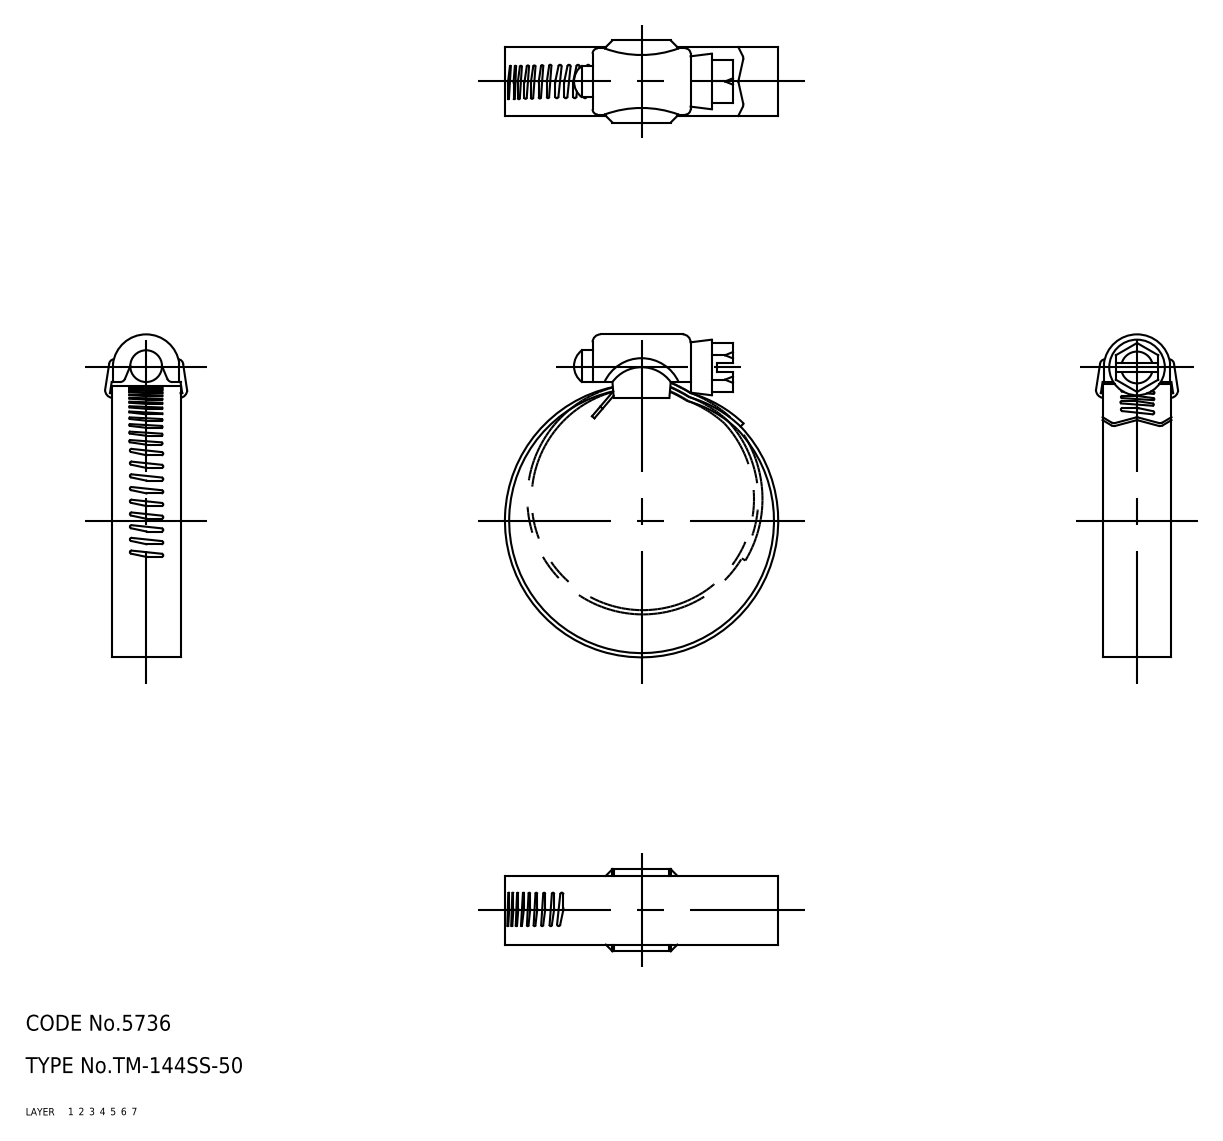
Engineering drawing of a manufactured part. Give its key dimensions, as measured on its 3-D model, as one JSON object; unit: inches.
{"part_name": "screw; holder; band; TM_144SS_50_20021_36", "step_written_by": "CADfix (AUTOMOTIVE_DESIGN)", "units": "inches", "bodies": {"solids": 3, "faces": 215, "planar": 0, "cylindrical": 0, "other": 215}, "overall_size": [2.401, 2.031, 0.615], "volume_in3": 0.249, "surface_area_in2": 11.59}
